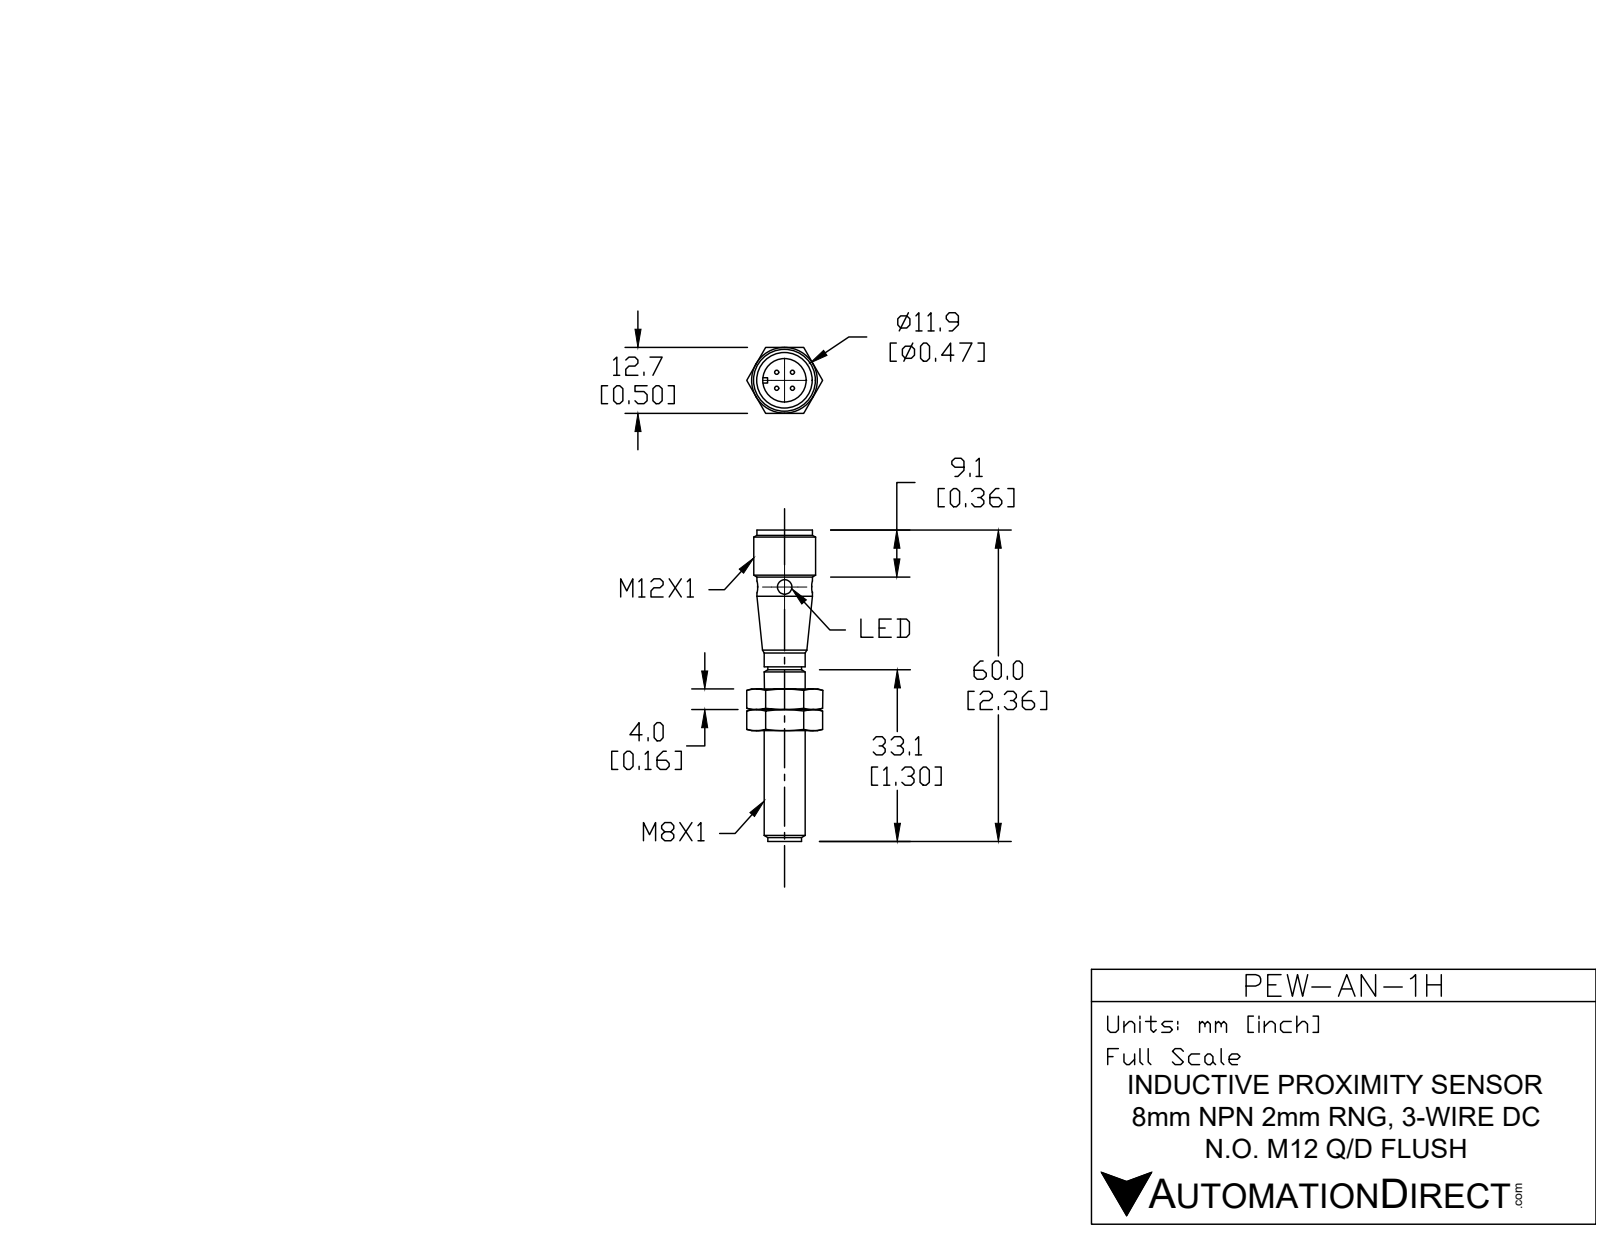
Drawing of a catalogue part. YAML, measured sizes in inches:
part_name: "PEW-AN-1H"
step_written_by: "SolidWorks 2017 (AUTOMOTIVE_DESIGN)"
units: inches
bodies: {solids: 3, faces: 103, planar: 27, cylindrical: 27, other: 49}
overall_size: [2.362, 0.591, 0.512]
volume: 0.267
surface_area: 4.763
round_holes:
  - {diameter: 0.098, count: 2}
  - {diameter: 0.272, count: 1}
  - {diameter: 0.331, count: 1}
round_bosses_or_shafts:
  - {diameter: 0.472, count: 1}
  - {diameter: 0.417, count: 1}
  - {diameter: 0.315, count: 1}
  - {diameter: 0.311, count: 1}
  - {diameter: 0.258, count: 1}
partial_cylinders:
  - {radius: 0.024, count: 1}
face_to_face_distances: [0.512, 0.157, 0.315, 1.382, 1.224, 1.539, 2.012, 0.787, 0.63, 0.472]
